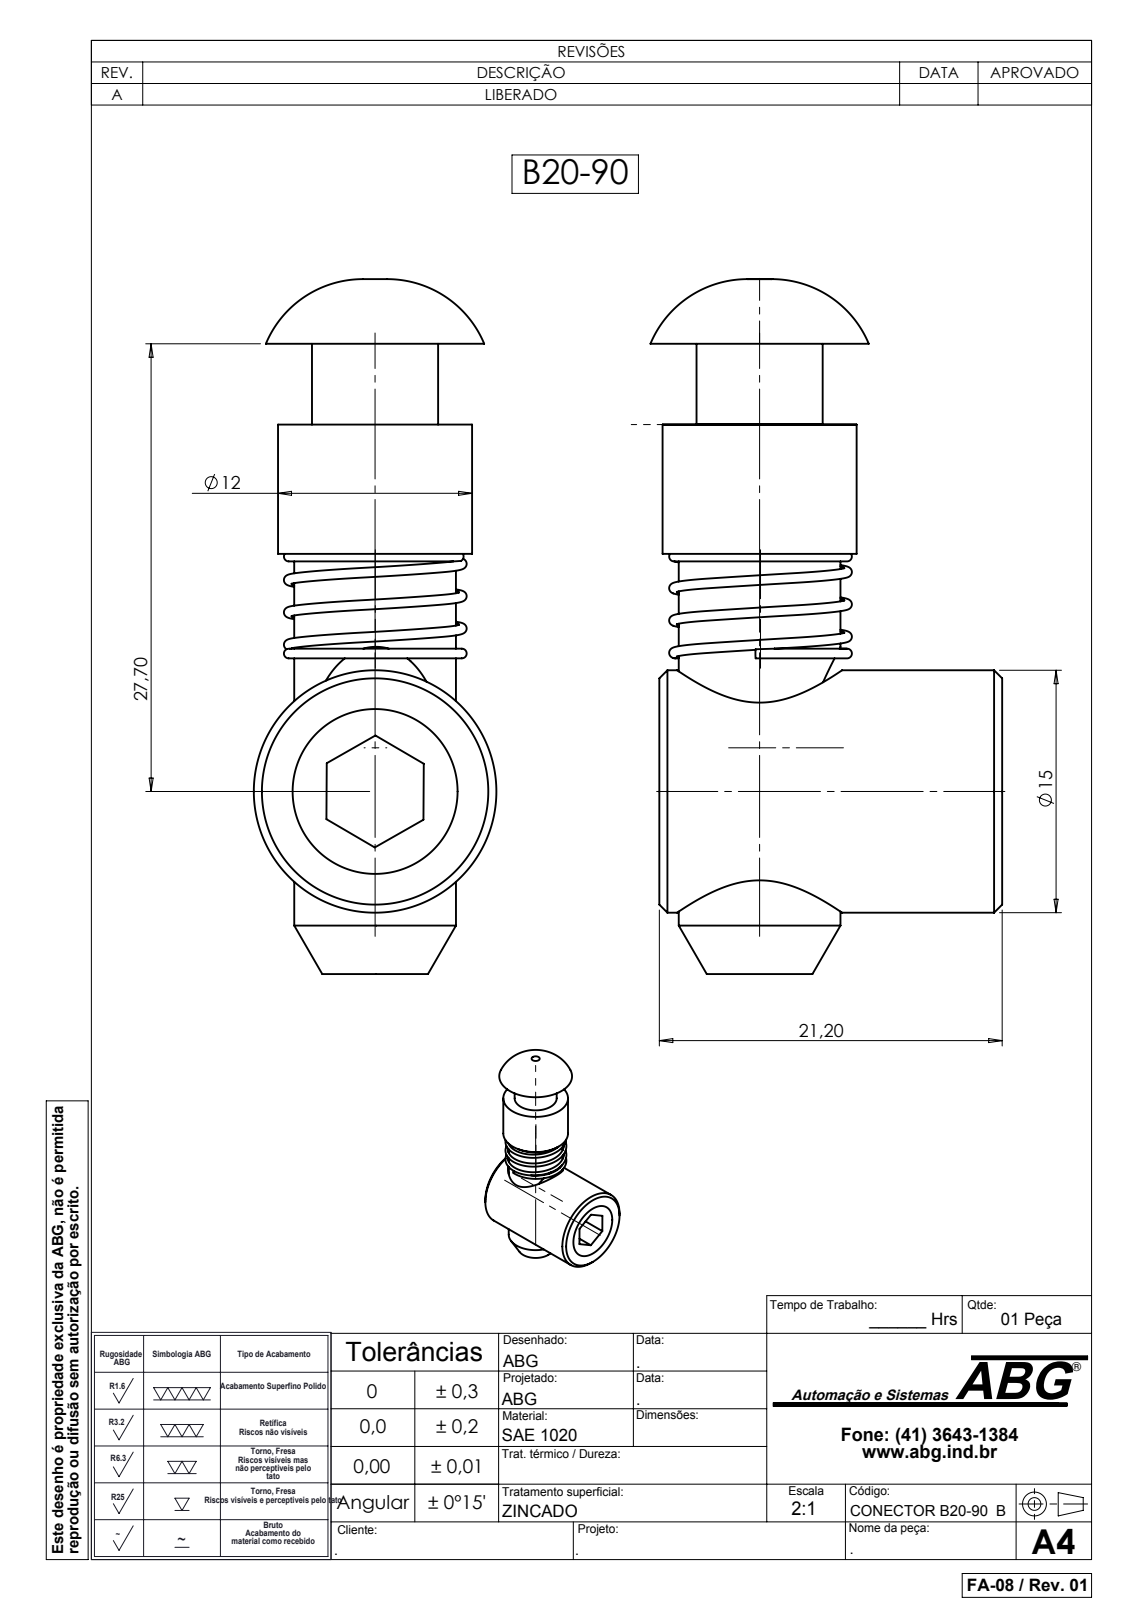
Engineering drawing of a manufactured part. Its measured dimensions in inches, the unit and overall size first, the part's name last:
Units: inches
Overall size (bounding box): 1.693 × 0.856 × 0.591
Round holes (diameter × count): ⌀0.402 ×2, ⌀0.407 ×1
Round bosses / shafts (diameter × count): ⌀0.472 ×2, ⌀0.591 ×1, ⌀0.394 ×1, ⌀0.307 ×1
Main face-to-face distances: 0.197, 0.82, 0.835, 0.014, 0.236, 0.315, 0.512, 1.024, 1.339, 1.535
Hole centre spacings: 0.018
Volume: 0.358 in³ · Surface area: 6.743 in²
Bodies: 4 solids, 67 faces (22 planar, 23 cylindrical, 22 other)
Part name (STEP PRODUCT): B20-90; BUCHA 120-10; MOLA 125-10; PARAFUSO 125-80 (+1 more)
STEP written by: SolidWorks 2007 (CONFIG_CONTROL_DESIGN)
